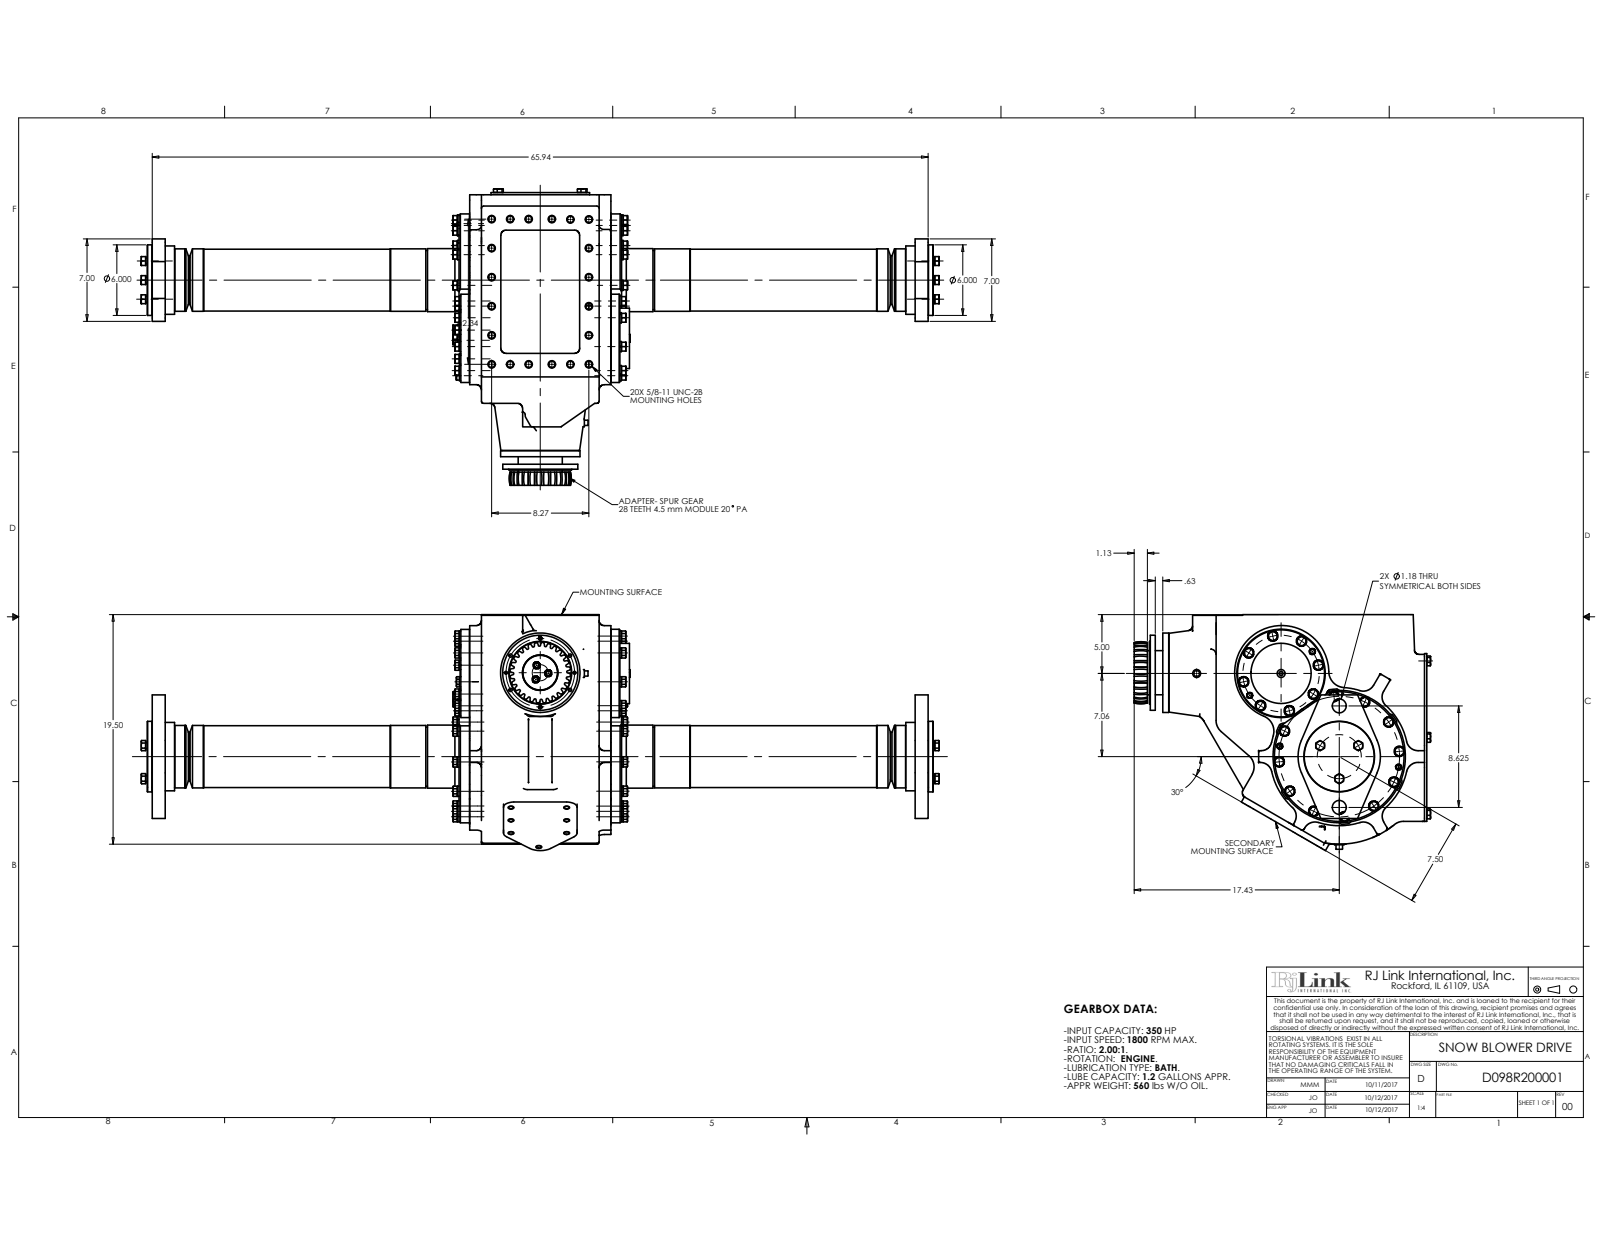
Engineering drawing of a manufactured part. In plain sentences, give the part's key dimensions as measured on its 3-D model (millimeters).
The part is named "PPSQG_375-18_1; OS3_740-47; D098059; D098R200001 (+8 more)". Its 3-D file was written by "SolidWorks 2017 (AUTOMOTIVE_DESIGN)". It is 88 solids with 6324 faces: 2428 planar, 2523 cylindrical and 1373 other. Overall it measures 1722.7 by 639.9 by 509.2 millimeters. Its volume is 16 280 000 cubic millimeters and its surface area 5 229 000 square millimeters. Round holes: 42 of diameter 13.5, 37 of diameter 13, 14 of diameter 7.1, 14 of diameter 14.2, 12 of diameter 11.2, 8 of diameter 10.3, 6 of diameter 11.1, 6 of diameter 13.9, 3 of diameter 11.1, 2 of diameter 4.8, 2 of diameter 5.2, 2 of diameter 5.6. Round bosses or shafts: 80 of diameter 12.7, 39 of diameter 19, 38 of diameter 10.7, 38 of diameter 9.5, 37 of diameter 22.1, 36 of diameter 11.1, 20 of diameter 15.9, 20 of diameter 13.5. Partial cylindrical surfaces (rounded edges, fillets, slot ends): 68 of radius 15.9, 49 of radius 11.2, 48 of radius 12.7, 48 of radius 38.1, 39 of radius 4.8, 29 of radius 31.8, 20 of radius 3, 16 of radius 0.8. The main face-to-face distances are 25.4, 279.4, 47.6, 257.2, 22.2, 231.8, 23.1, 48.5, 70.8, 280.3. The hole center spacings are 130.2, 130.2, 73.9, 225.5, 74, 184.1, 260.4, 251.5.
